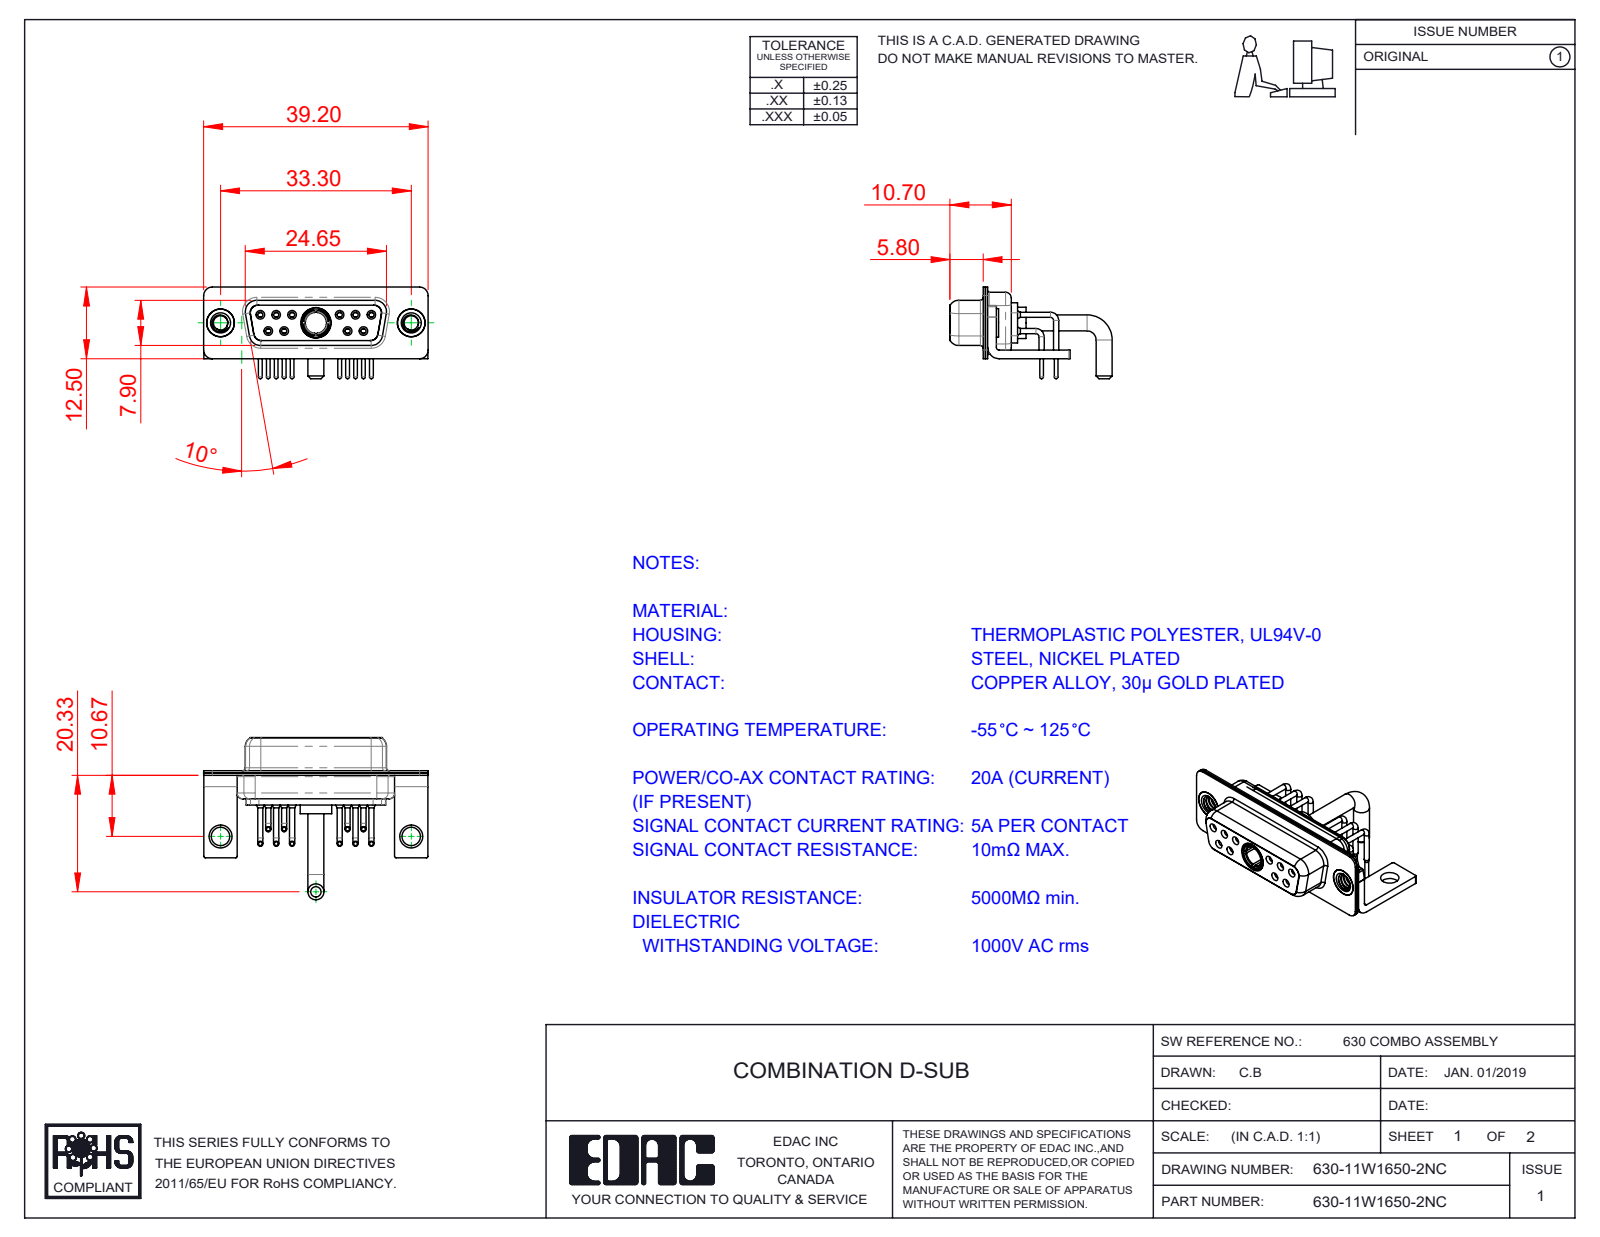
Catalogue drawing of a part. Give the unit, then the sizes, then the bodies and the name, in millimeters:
Units: millimetres
Overall size (bounding box): 39.2 × 28.33 × 16
Round holes (diameter × count): ⌀0.9 ×10, ⌀1.1 ×10, ⌀1.5 ×10, ⌀2 ×10, ⌀1.7 ×6, ⌀1.6 ×4, ⌀4.85 ×3, ⌀2.5 ×2, ⌀3.2 ×2, ⌀4 ×2, ⌀4.05 ×2, ⌀3.7 ×1
Round bosses / shafts (diameter × count): ⌀0.9 ×10, ⌀0.65 ×10, ⌀1.6 ×6, ⌀5 ×2, ⌀4.95 ×2, ⌀4.8 ×2, ⌀2.8 ×2, ⌀5.5 ×1
Partial cylindrical surfaces — rounded edges, fillets, slot ends (radius × count): R0.25 ×16, R1.5 ×16, R2 ×13, R1.35 ×12, R1.6 ×8, R0.5 ×5, R0.6 ×4, R0.65 ×4
Main face-to-face distances: 0.4, 0.8, 1.4, 0.45, 8.45, 1.5, 1.8, 8.9, 6.2, 2.3
Hole centre spacings: 3.16, 2.77, 13.85, 11.08, 16.62, 5.03, 5.04, 5.54
Volume: 2 952 mm³ · Surface area: 6 923 mm²
Bodies: 19 solids, 925 faces (266 planar, 410 cylindrical, 249 other)
Part name (STEP PRODUCT): Power Socket_Ext 20A RA; 630Combo Stabilizer Bracket; 630Combo Contact Row 2; 630Combo Shell Front_15 Contacts (+5 more)
STEP written by: SolidWorks 2020 (CONFIG_CONTROL_DESIGN)
